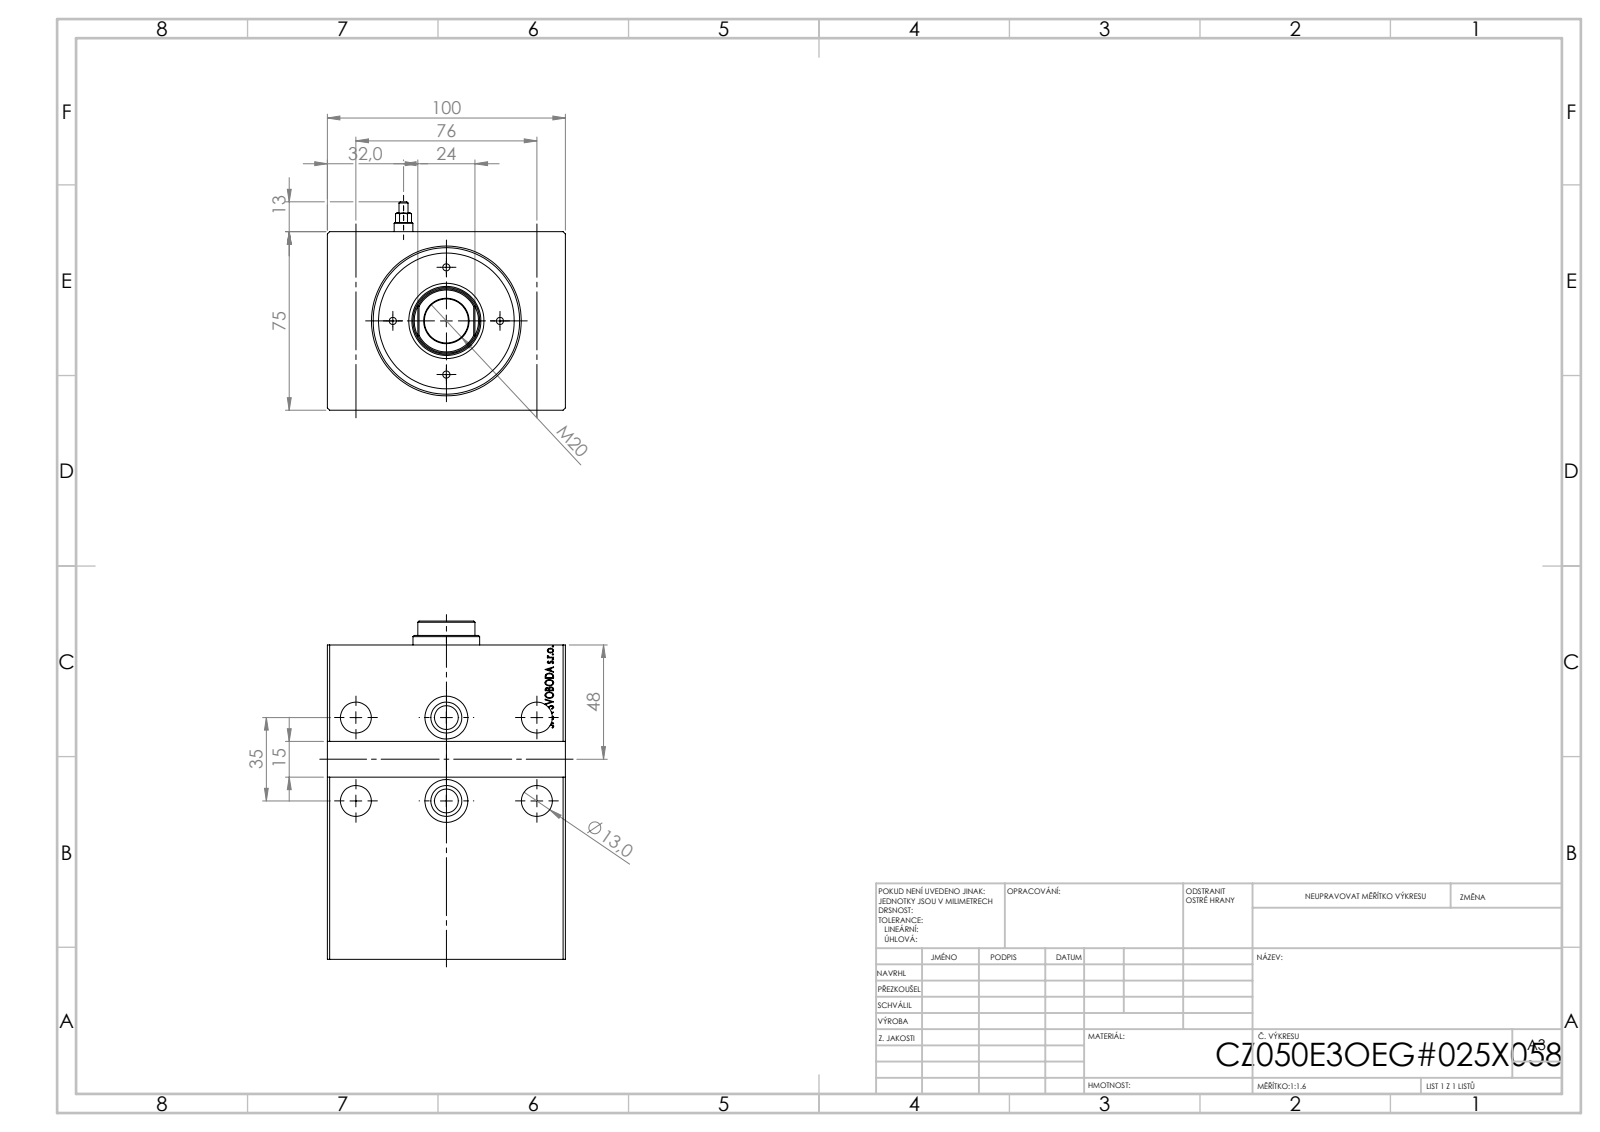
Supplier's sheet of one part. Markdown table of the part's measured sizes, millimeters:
| quantity | value |
| --- | --- |
| STEP written by | SolidWorks 2019 (CONFIG_CONTROL_DESIGN) |
| units | millimeters |
| bodies | 1 solid, 775 faces (375 planar, 30 cylindrical, 370 other) |
| overall size | 132 × 100 × 75 |
| volume | 711 212 mm³ |
| surface area | 91 409 mm² |
| round holes (diameter × count) | 13 × 4, 8 × 2, 10 × 2, 18 × 2, 36 × 1, 50 × 1, 61.5 × 1 |
| round bosses / shafts (diameter × count) | 13 × 2 |
| main face-to-face distances | 75, 100, 132, 114.2, 17.8, 2, 73, 131.8, 17.6, 10 |
| hole center spacings | 38, 51.66, 35, 76, 83.67, 19.14, 21.03, 33.71 |
